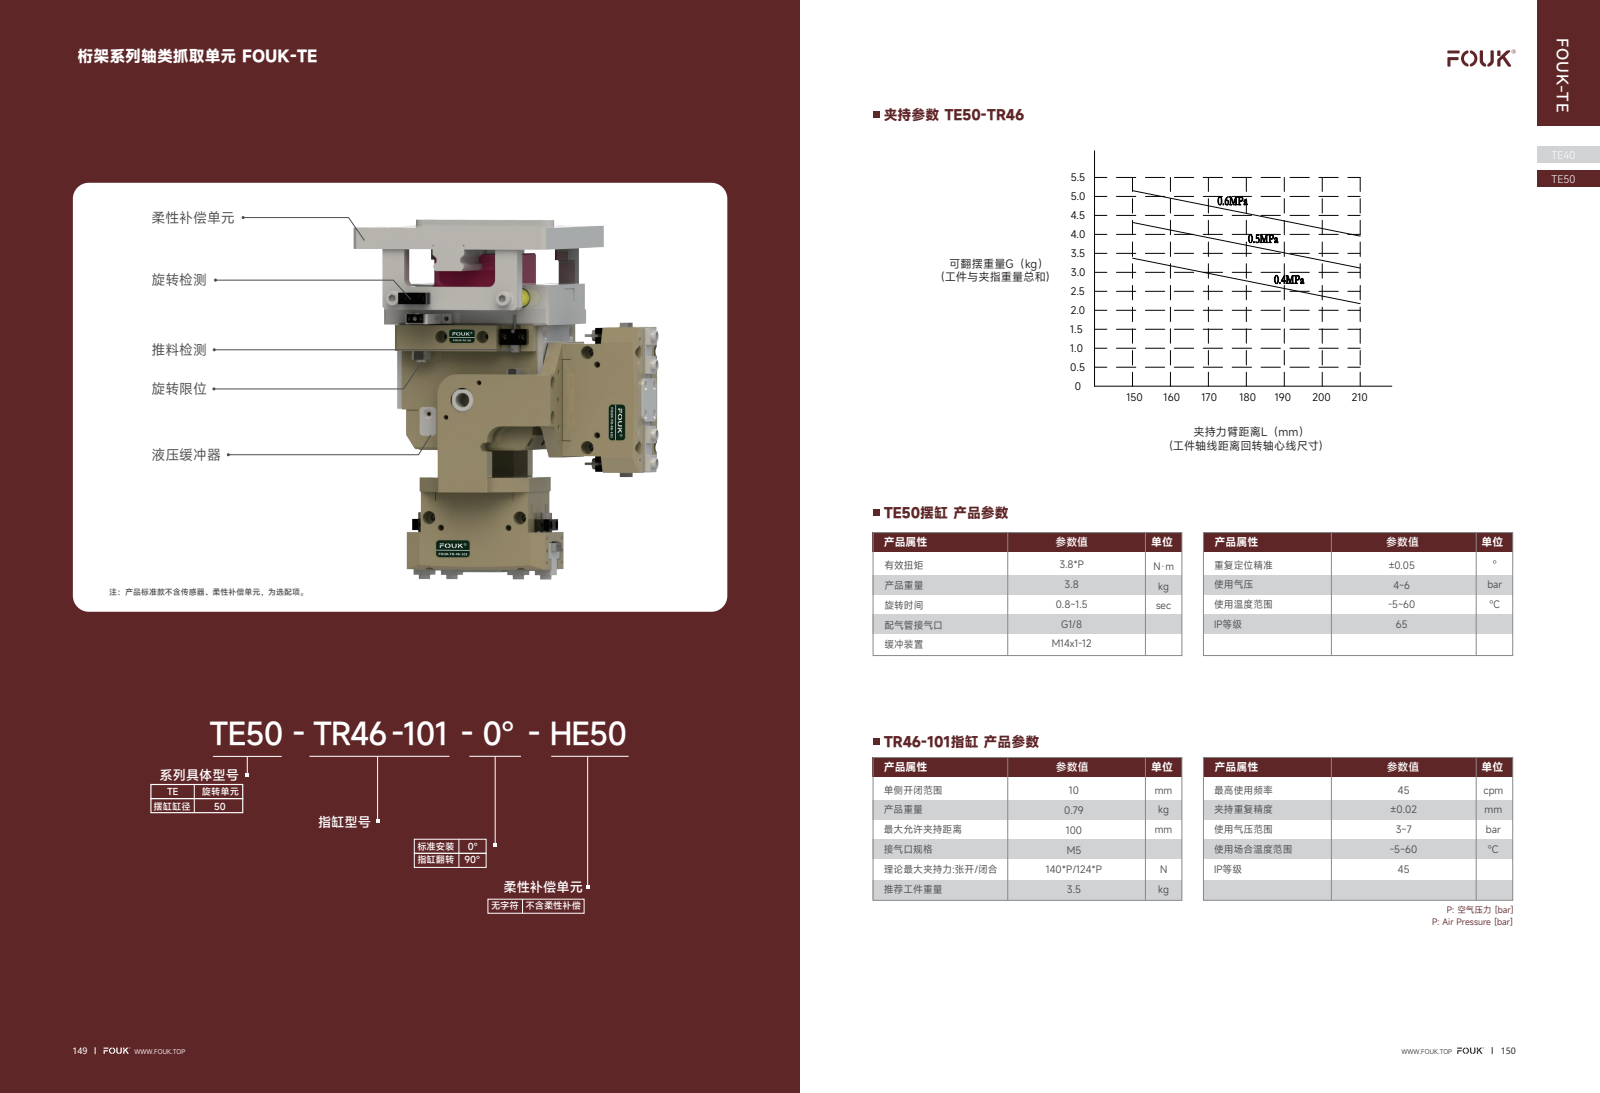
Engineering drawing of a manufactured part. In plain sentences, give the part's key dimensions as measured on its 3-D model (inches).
The part is named "TE50-tr50.sldasm-Part-21; TE50-tr50.sldasm-Part-12; 25x12-R3; TE50-tr50.sldasm-Part-8 (+6 more)". Its 3-D file was written by "SolidWorks 2018 (CONFIG_CONTROL_DESIGN)". It is 25 solids with 1219 faces: 507 planar, 410 cylindrical and 302 other. Overall it measures 4.736 by 4.606 by 4.331 inches. Its volume is 55.88 cubic inches and its surface area 270.2 square inches. Round holes: 16 of diameter 0.165, 8 of diameter 0.157, 6 of diameter 0.098, 6 of diameter 0.138, 6 of diameter 0.236, 6 of diameter 0.268, 4 of diameter 0.197, 2 of diameter 0.13, 2 of diameter 0.194, 2 of diameter 0.339, 1 of diameter 0.079, 1 of diameter 0.177. Round bosses or shafts: 4 of diameter 0.236, 2 of diameter 0.315, 2 of diameter 0.276, 2 of diameter 0.226, 2 of diameter 0.079, 1 of diameter 1.213, 1 of diameter 0.102, 1 of diameter 0.071. Partial cylindrical surfaces (rounded edges, fillets, slot ends): 28 of radius 0.039, 18 of radius 0.005, 12 of radius 0.005, 9 of radius 0.394, 8 of radius 0.079, 8 of radius 0.098, 5 of radius 0.012, 5 of radius 0.118. The main face-to-face distances are 3.543, 0.63, 4.173, 0.472, 0.157, 0.394, 3.858, 2.913, 0.709, 3.386. The hole center spacings are 2.492, 0.752, 1.444, 2.12, 2.78, 0.78, 1.496, 1.499.
